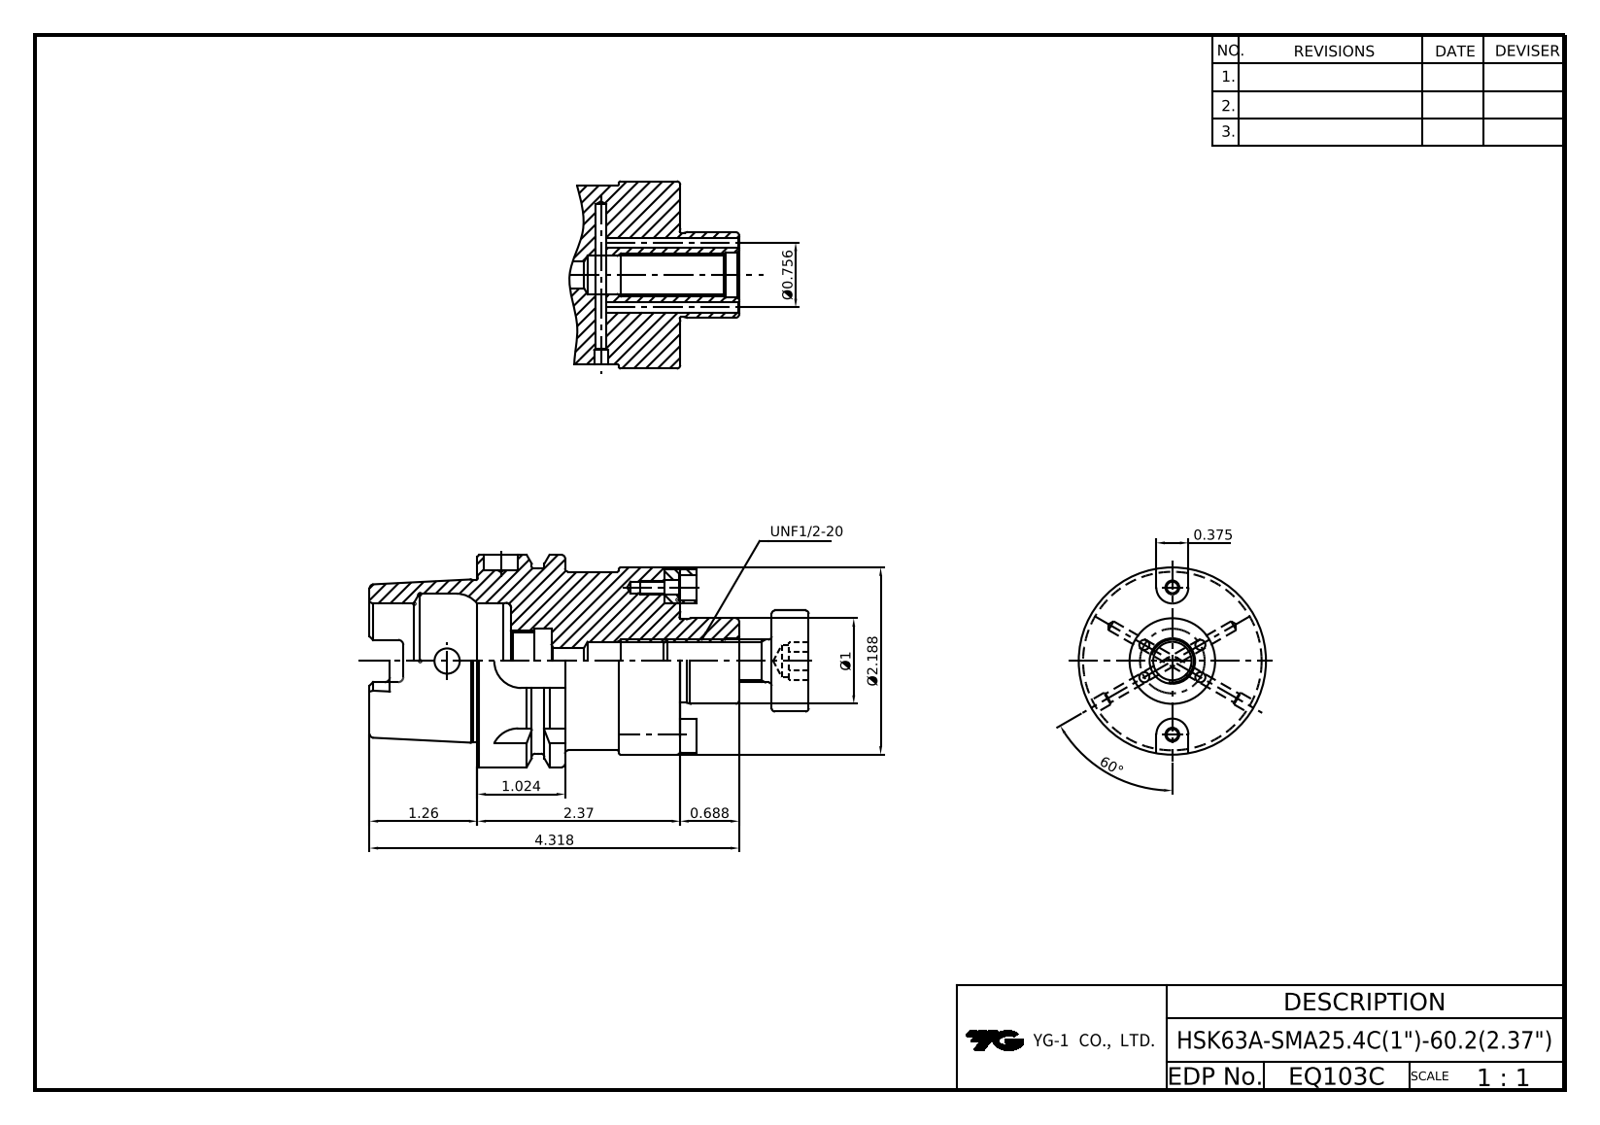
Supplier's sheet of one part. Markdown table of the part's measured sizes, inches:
| quantity | value |
| --- | --- |
| part name | LO-HSK63A-SMA25.4C-60.2; COLLAR BOLT-UNF1_2-20x32L; DRIVE KEY-9.52x9.52x10.2; HEX'' WRENCH BOLT-UNC#8-32x3_8L |
| STEP written by | Autodesk Inventor 2025 (AP242_MANAGED_MODEL_BASED_3D_ENGINEERING_MIM_LF) |
| units | inches |
| bodies | 6 solids, 223 faces (95 planar, 57 cylindrical, 71 other) |
| overall size | 4.81 × 2.48 × 2.48 |
| volume | 10.84 in³ |
| surface area | 61.41 in² |
| round holes (diameter × count) | 0.118 × 4, 0.295 × 3, 0.13 × 2, 0.177 × 2, 0.315 × 1, 0.375 × 1, 0.394 × 1, 0.446 × 1, 0.531 × 1, 0.666 × 1, 0.748 × 1, 1.339 × 1 |
| round bosses / shafts (diameter × count) | 0.27 × 2, 0.164 × 2, 2.48 × 1, 2.25 × 1, 2.165 × 1, 2.087 × 1, 1.891 × 1, 1.181 × 1 |
| partial cylindrical surfaces (radius × count) | 0.059 × 6, 0.113 × 4, 0.187 × 4, 0.315 × 4 |
| main face-to-face distances | 2.37, 0.63, 1.26, 0.394, 1.024, 1.654, 1.976, 3.55, 3.157, 1.18 |
| hole center spacings | 0.755, 0.378, 1.107, 1.108, 0.654, 0.756, 0.869, 0.869 |
